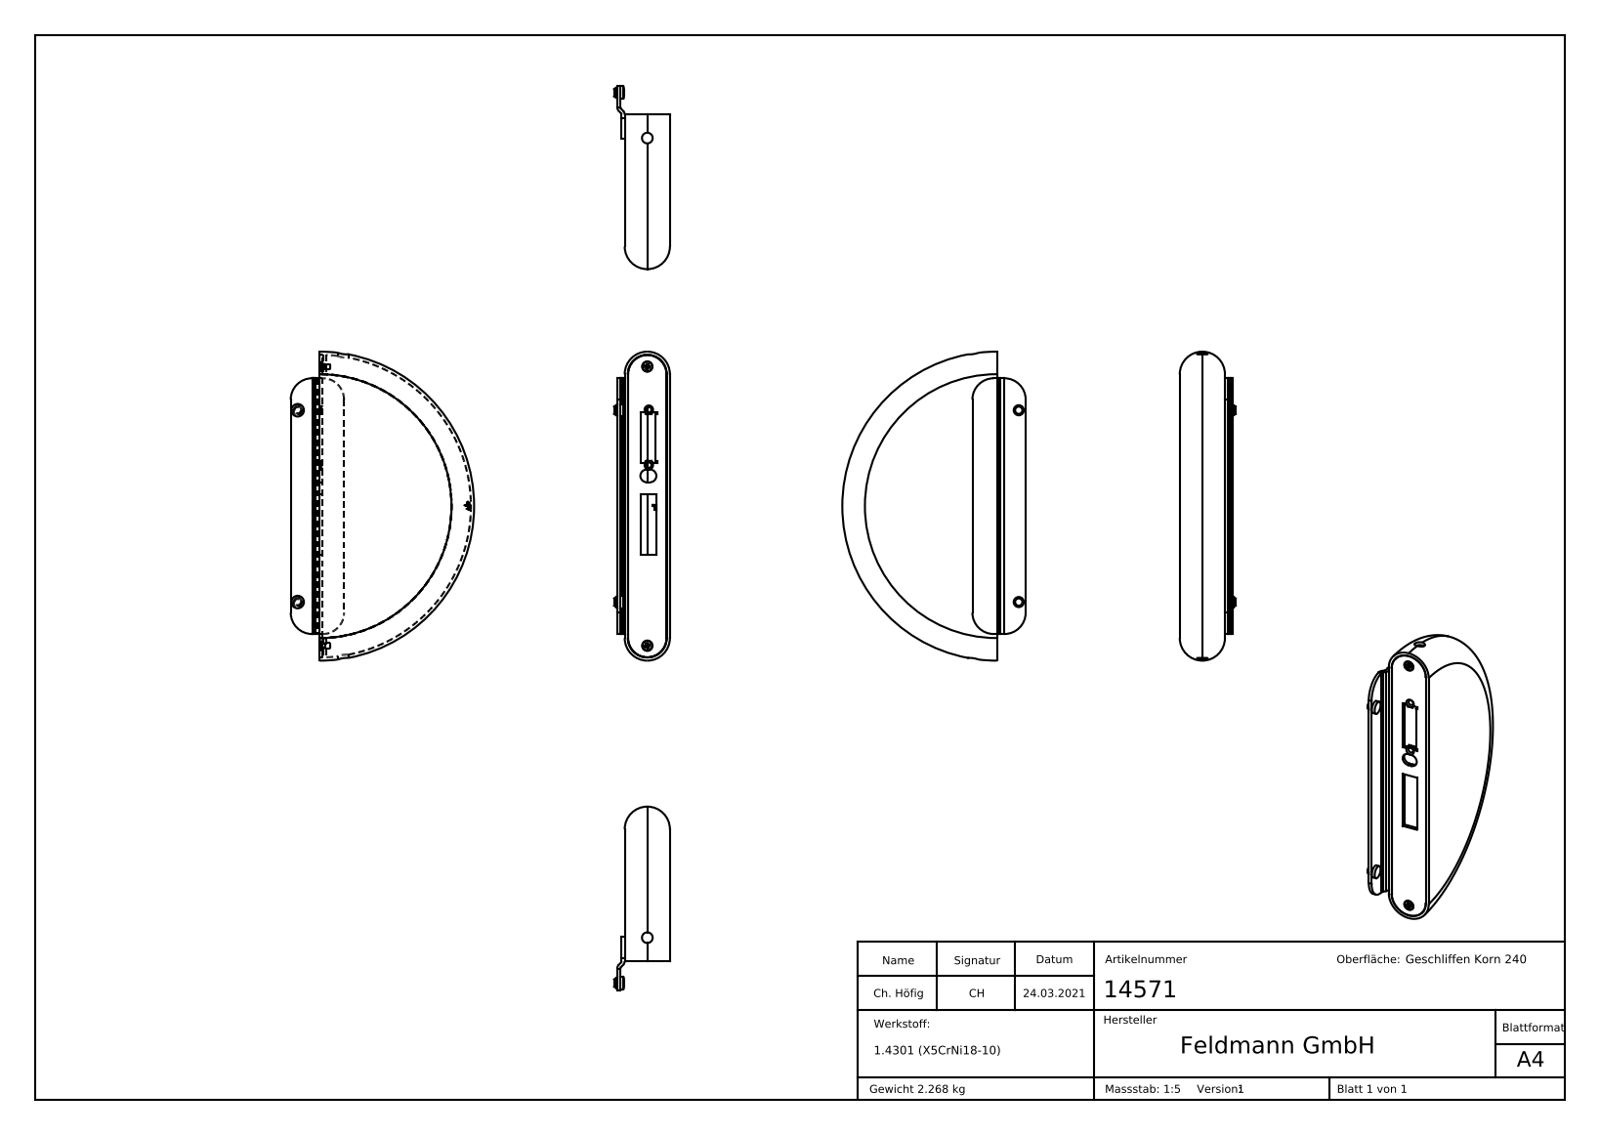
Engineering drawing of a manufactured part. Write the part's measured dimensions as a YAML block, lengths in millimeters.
part_name: "DIN 965; 14571 Teil2_14571 Teil2; 14571 Teil3; 14571 Teil1 (+5 more)"
step_written_by: "SolidWorks 2018 (CONFIG_CONTROL_DESIGN)"
units: millimeters
bodies: {solids: 6, faces: 394, planar: 193, cylindrical: 53, other: 148}
overall_size: [9500, 6487.49, 6119.02]
volume: 288168
surface_area: 188837
round_holes:
  - {diameter: 4.2, count: 2}
  - {diameter: 6.8, count: 2}
  - {diameter: 8, count: 2}
  - {diameter: 10, count: 1}
round_bosses_or_shafts:
  - {diameter: 11.8, count: 2}
  - {diameter: 9.5, count: 2}
  - {diameter: 9, count: 2}
  - {diameter: 6, count: 2}
  - {diameter: 5, count: 2}
  - {diameter: 4.6, count: 2}
partial_cylinders:
  - {radius: 20, count: 4}
  - {radius: 2, count: 2}
  - {radius: 5, count: 2}
  - {radius: 6, count: 2}
  - {radius: 18, count: 2}
face_to_face_distances: [3, 39.4, 42.4, 36.4, 7, 4, 46.4, 6, 45.4, 10]
hole_center_spacings: [180, 262]
